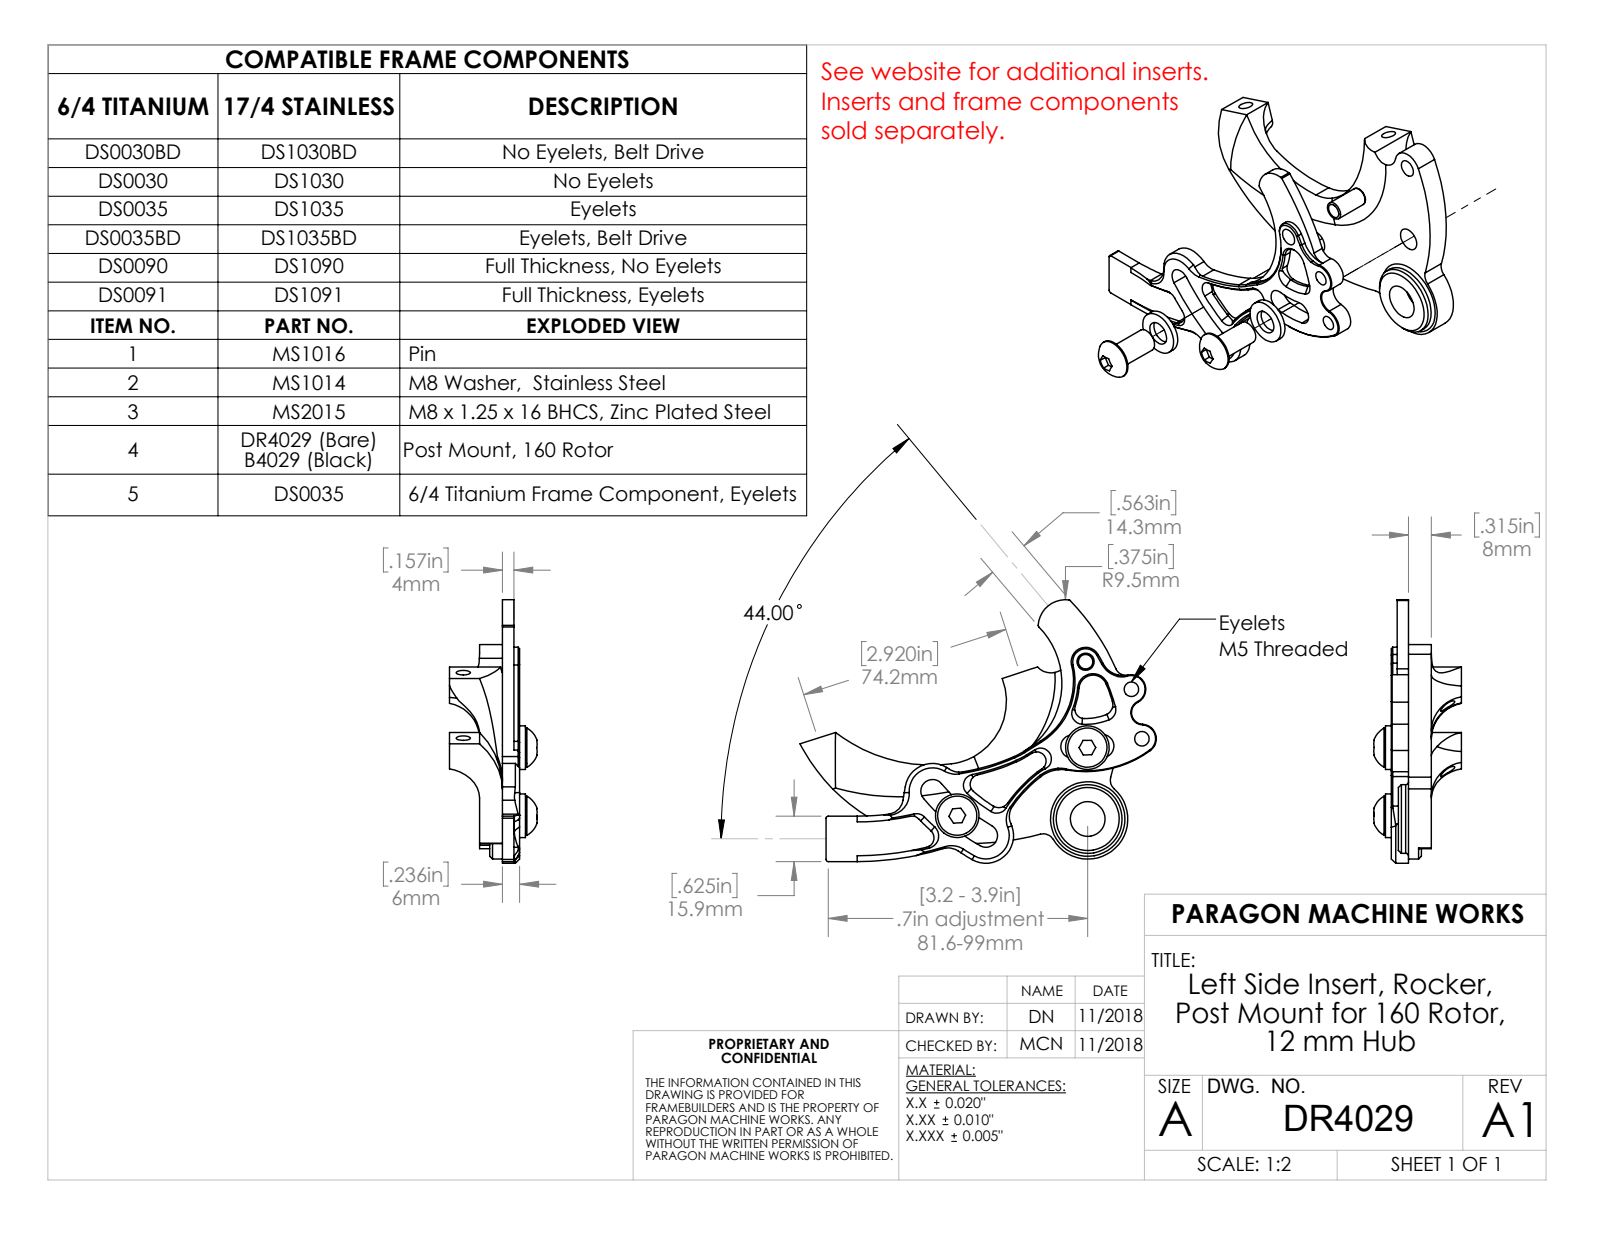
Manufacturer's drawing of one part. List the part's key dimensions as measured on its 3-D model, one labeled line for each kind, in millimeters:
Part name (STEP PRODUCT): DR4029
STEP written by: SolidWorks 2018 (AUTOMOTIVE_DESIGN)
Units: millimetres
Bodies: 1 solid, 101 faces (19 planar, 69 cylindrical, 13 other)
Overall size (bounding box): 111.1 × 74.21 × 22
Volume: 27 769 mm³ · Surface area: 13 836 mm²
Round holes (diameter × count): ⌀5 ×2, ⌀5.99 ×1, ⌀8 ×1, ⌀8 ×1, ⌀12.13 ×1
Round bosses / shafts (diameter × count): ⌀24 ×1
Partial cylindrical surfaces — rounded edges, fillets, slot ends (radius × count): R3.81 ×9, R12.7 ×5, R17.41 ×3, R1 ×2, R4 ×2, R6.35 ×2, R4.04 ×1, R4.19 ×1
Main face-to-face distances: 8, 4.4, 3.6, 3.5, 0.9, 4.5, 11.5, 7.1, 10.5, 14
Hole centre spacings: 24.92, 30, 45.59, 51.29, 54.92, 70.01, 74.17
